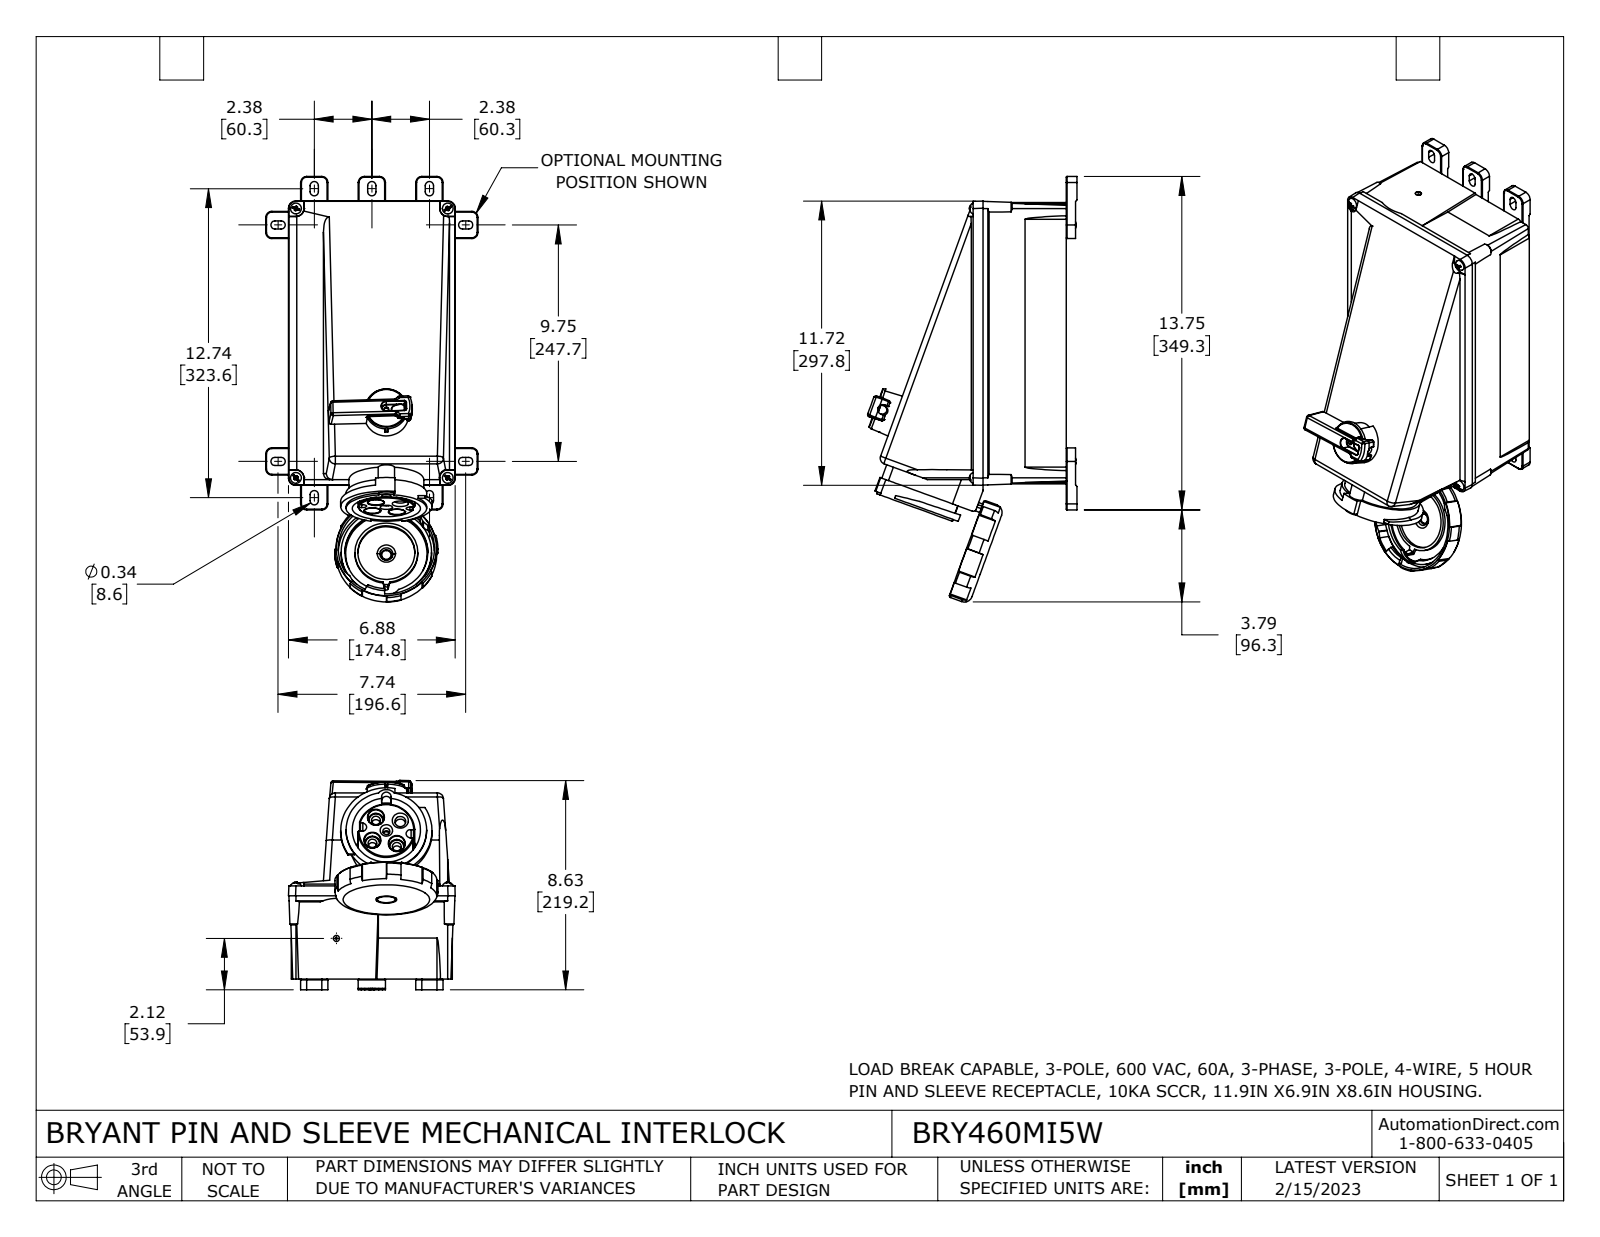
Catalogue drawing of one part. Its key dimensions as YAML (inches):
part_name: "BRY460MI5W"
step_written_by: "SolidWorks 2021 (CONFIG_CONTROL_DESIGN)"
units: inches
bodies: {solids: 17, faces: 2005, planar: 760, cylindrical: 642, other: 603}
overall_size: [17.549, 8.635, 6.88]
volume: 426.5
surface_area: 821.7
round_holes:
  - {diameter: 0.281, count: 5}
  - {diameter: 0.12, count: 3}
  - {diameter: 0.366, count: 3}
  - {diameter: 0.101, count: 2}
  - {diameter: 0.125, count: 2}
  - {diameter: 0.157, count: 2}
  - {diameter: 0.25, count: 2}
  - {diameter: 0.169, count: 1}
  - {diameter: 0.19, count: 1}
  - {diameter: 0.27, count: 1}
  - {diameter: 0.28, count: 1}
  - {diameter: 0.445, count: 1}
round_bosses_or_shafts:
  - {diameter: 0.433, count: 5}
  - {diameter: 0.263, count: 2}
  - {diameter: 3.73, count: 1}
  - {diameter: 3.323, count: 1}
  - {diameter: 3.091, count: 1}
  - {diameter: 2.592, count: 1}
  - {diameter: 2.342, count: 1}
  - {diameter: 0.8, count: 1}
partial_cylinders:
  - {radius: 0.015, count: 135}
  - {radius: 0.03, count: 41}
  - {radius: 0.08, count: 30}
  - {radius: 0.02, count: 24}
  - {radius: 0.09, count: 19}
  - {radius: 0.25, count: 16}
  - {radius: 0.075, count: 12}
  - {radius: 0.17, count: 10}
face_to_face_distances: [3.44, 6.646, 11.594, 5.528, 0.14, 5.388, 0.15, 6.818, 5.363, 0.025]
hole_center_spacings: [1.595, 0.71, 0.71, 0.59, 0.59, 1.42, 1.595, 4.172]
